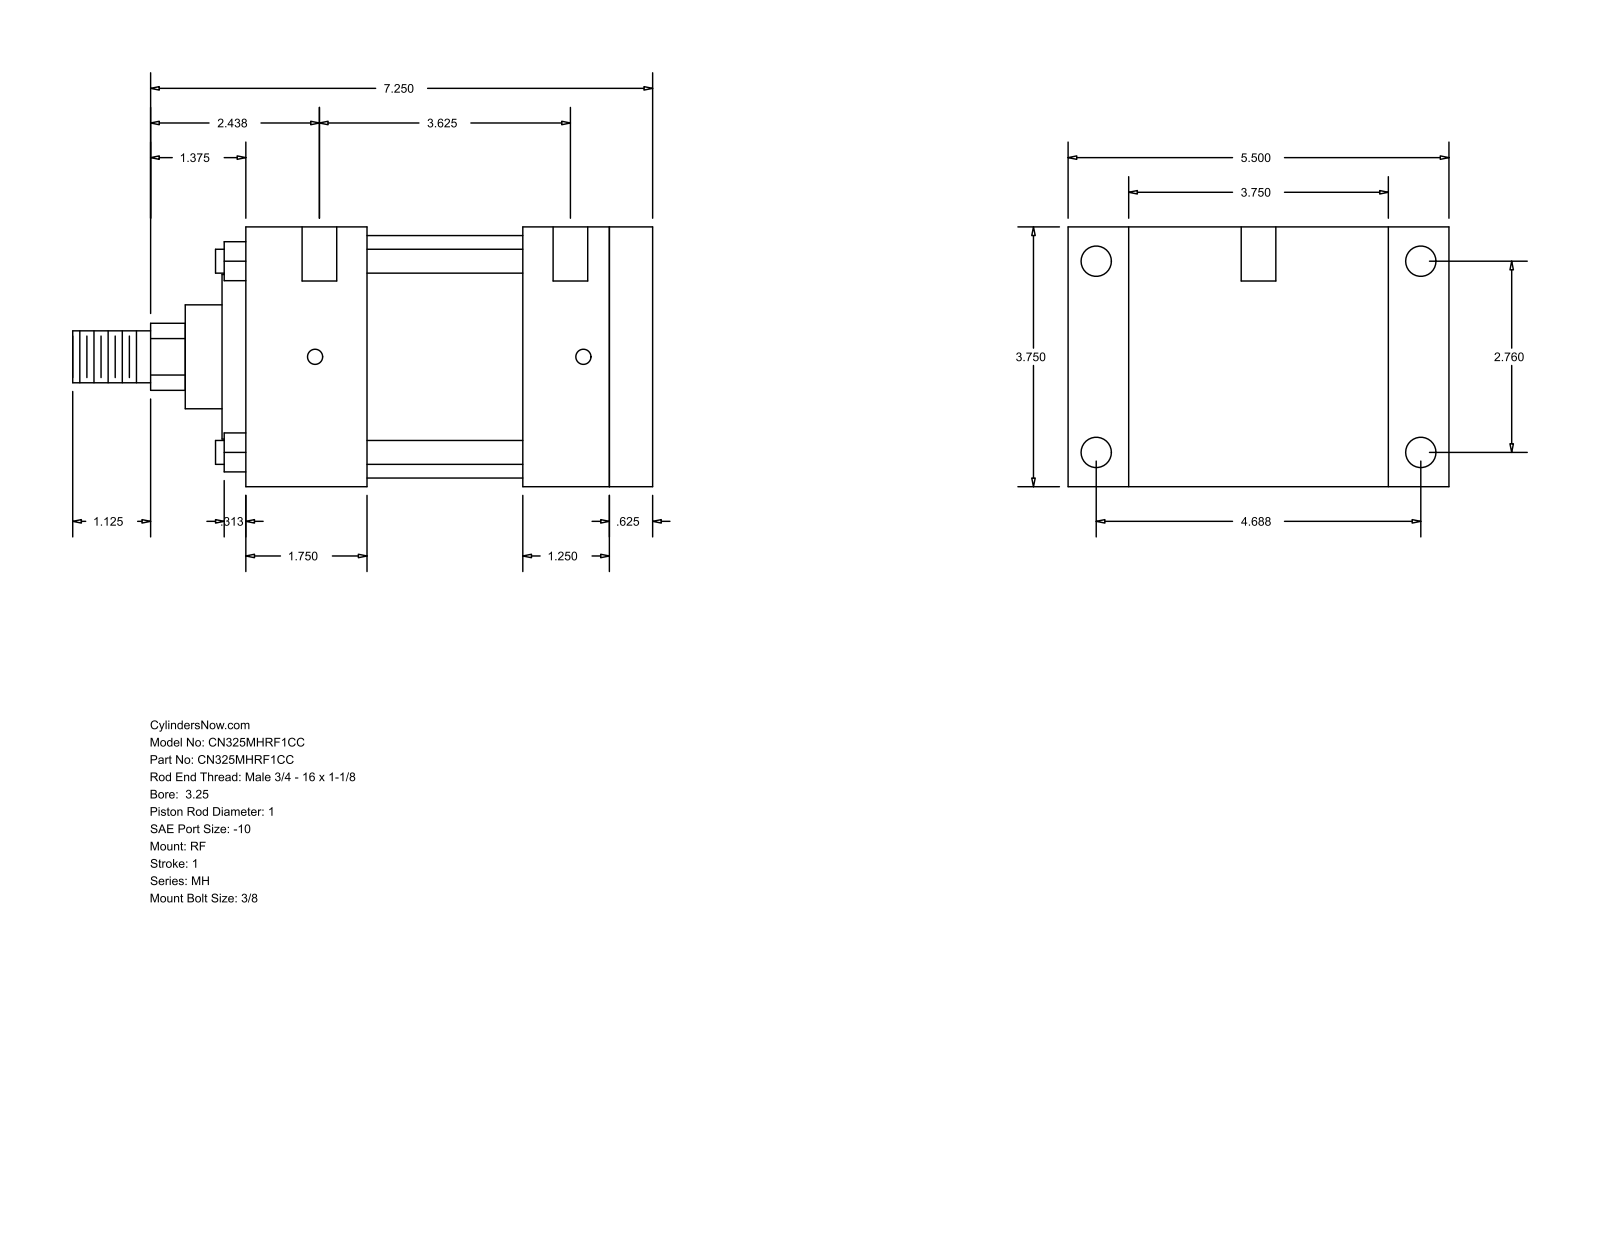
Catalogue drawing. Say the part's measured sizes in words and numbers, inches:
The part is named "MH_RF__0325_1". Its 3-D file was written by "GSSL Pune (CONFIG_CONTROL_DESIGN)". It is 0 solids with 94 faces: 65 planar, 29 cylindrical and 0 other. Overall it measures 8.375 by 5.5 by 3.75 inches. Round holes: 4 of diameter 0.219, 4 of diameter 0.438, 2 of diameter 0.5. Round bosses or shafts: 4 of diameter 0.345, 1 of diameter 3.5, 1 of diameter 2.375, 1 of diameter 1.5, 1 of diameter 1, 1 of diameter 0.75. Partial cylindrical surfaces (rounded edges, fillets, slot ends): 1 of radius 0.484. The main face-to-face distances are 3.75, 5.875, 5.25, 0.625, 0.875, 4.625, 1.75, 3.5, 4.125, 4. The hole center spacings are 2.76, 3.875, 4.687, 5.439, 0.062, 0.187, 3.625, 3.687.
